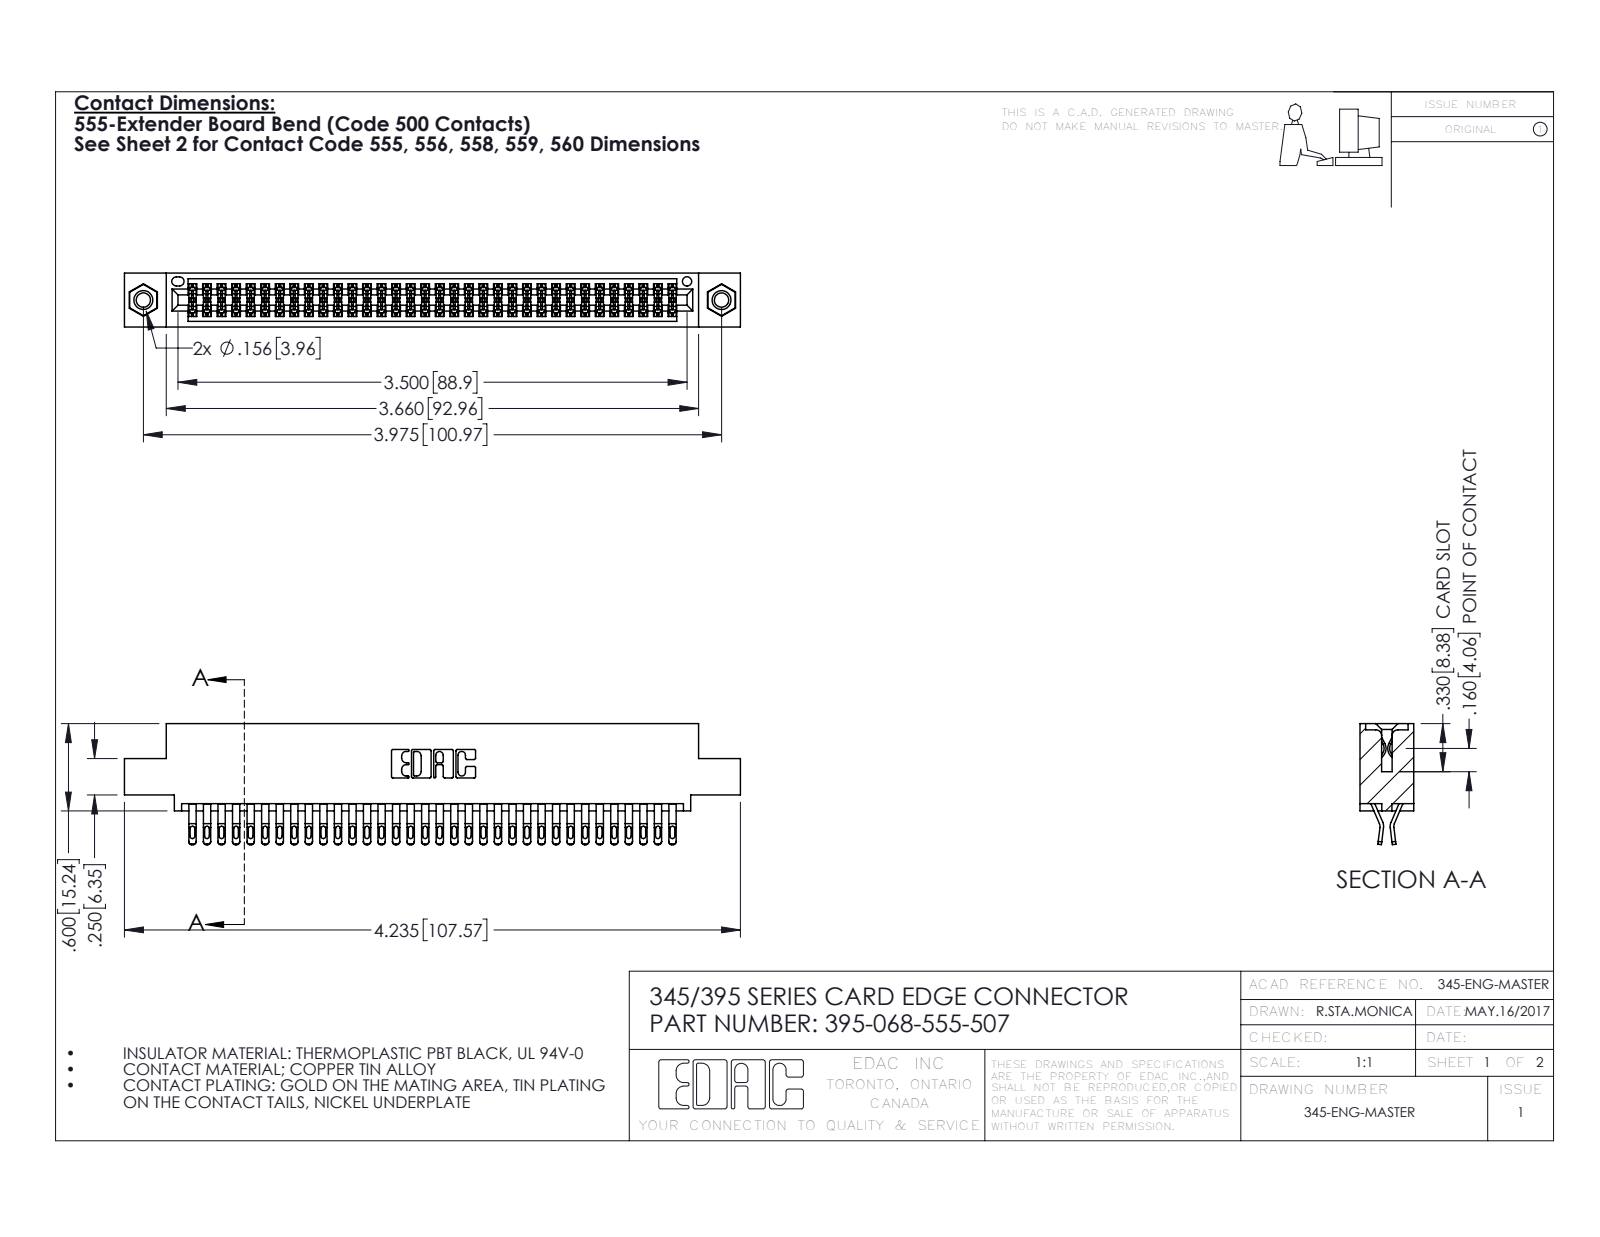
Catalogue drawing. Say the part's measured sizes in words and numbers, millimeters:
The part is named "345 Part_0.110 Offset - 0.156 Dia-TI; 345-250-001_345-250-005-103; 345-292-001_555 Tail; 395-068-555-507". Its 3-D file was written by "SolidWorks 2016 (CONFIG_CONTROL_DESIGN)". It is 71 solids with 3998 faces: 2224 planar, 1758 cylindrical and 16 other. Overall it measures 107.6 by 21.1 by 9.4 millimeters. Its volume is 10 500 cubic millimeters and its surface area 16 150 square millimeters. Round holes: 2 of diameter 2.5, 2 of diameter 3.2, 2 of diameter 4, 1 of diameter 1.6. Round bosses or shafts: 2 of diameter 3.9. Partial cylindrical surfaces (rounded edges, fillets, slot ends): 170 of radius 0.4, 136 of radius 0.5, 102 of radius 0.2, 22 of radius 0.3, 6 of radius 0.2, 6 of radius 0.8, 3 of radius 0.7, 2 of radius 0.3. The main face-to-face distances are 1.8, 7.6, 9.4, 5.1, 0.6, 2.5, 6.9, 5.7, 4.4, 3.8. The hole center spacings are 6.9, 95, 101.
